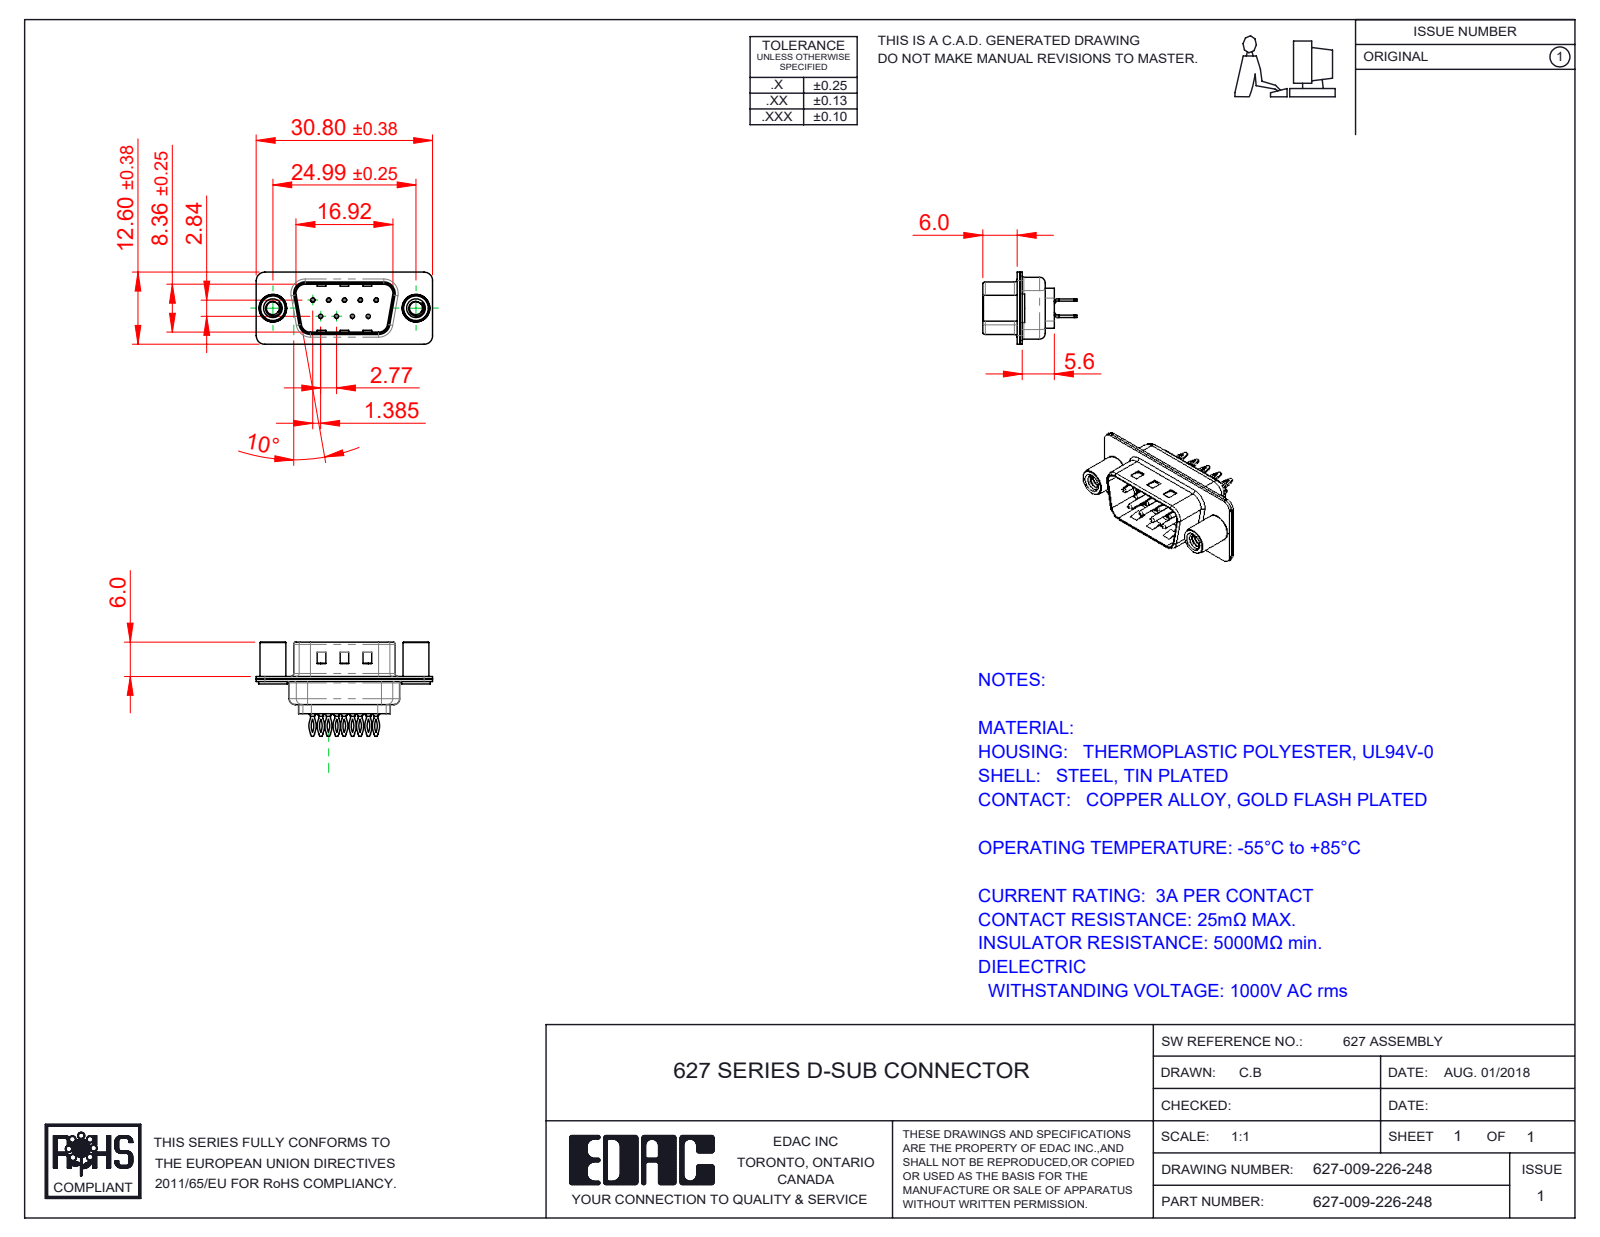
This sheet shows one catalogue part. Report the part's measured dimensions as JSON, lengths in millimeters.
{"part_name": "627 Housing_09 LP; 627 Shell Front_09 Contacts; 627 4-40 Threaded Standoff; 627 Shell Rear_09 Contacts (+3 more)", "step_written_by": "SolidWorks 2020 (CONFIG_CONTROL_DESIGN)", "units": "millimeters", "bodies": {"solids": 14, "faces": 1022, "planar": 289, "cylindrical": 436, "other": 297}, "overall_size": [30.8, 16.45, 12.6], "volume_mm3": 1375, "surface_area_mm2": 4100, "round_holes": [[0.35, 9], [1.1, 9], [1.6, 9], [2.26, 2], [4, 2], [4.8, 2]], "round_bosses_or_shafts": [[2, 9], [1.5, 9], [0.75, 9], [5, 2], [4.9, 2], [4.5, 2]], "partial_cylinders_radius": [[1.5, 18], [2.92, 18], [3.33, 18], [2, 12], [0.5, 8], [1.6, 8], [0.25, 4], [0.6, 4]], "face_to_face_distances": [0.4, 0.45, 0.9, 0.82, 9.58, 1.4, 8.76, 0.5, 1.5, 6.05], "hole_center_spacings": [3.16, 2.77, 5.54, 5.03, 5.04, 8.31, 7.48, 7.49]}
